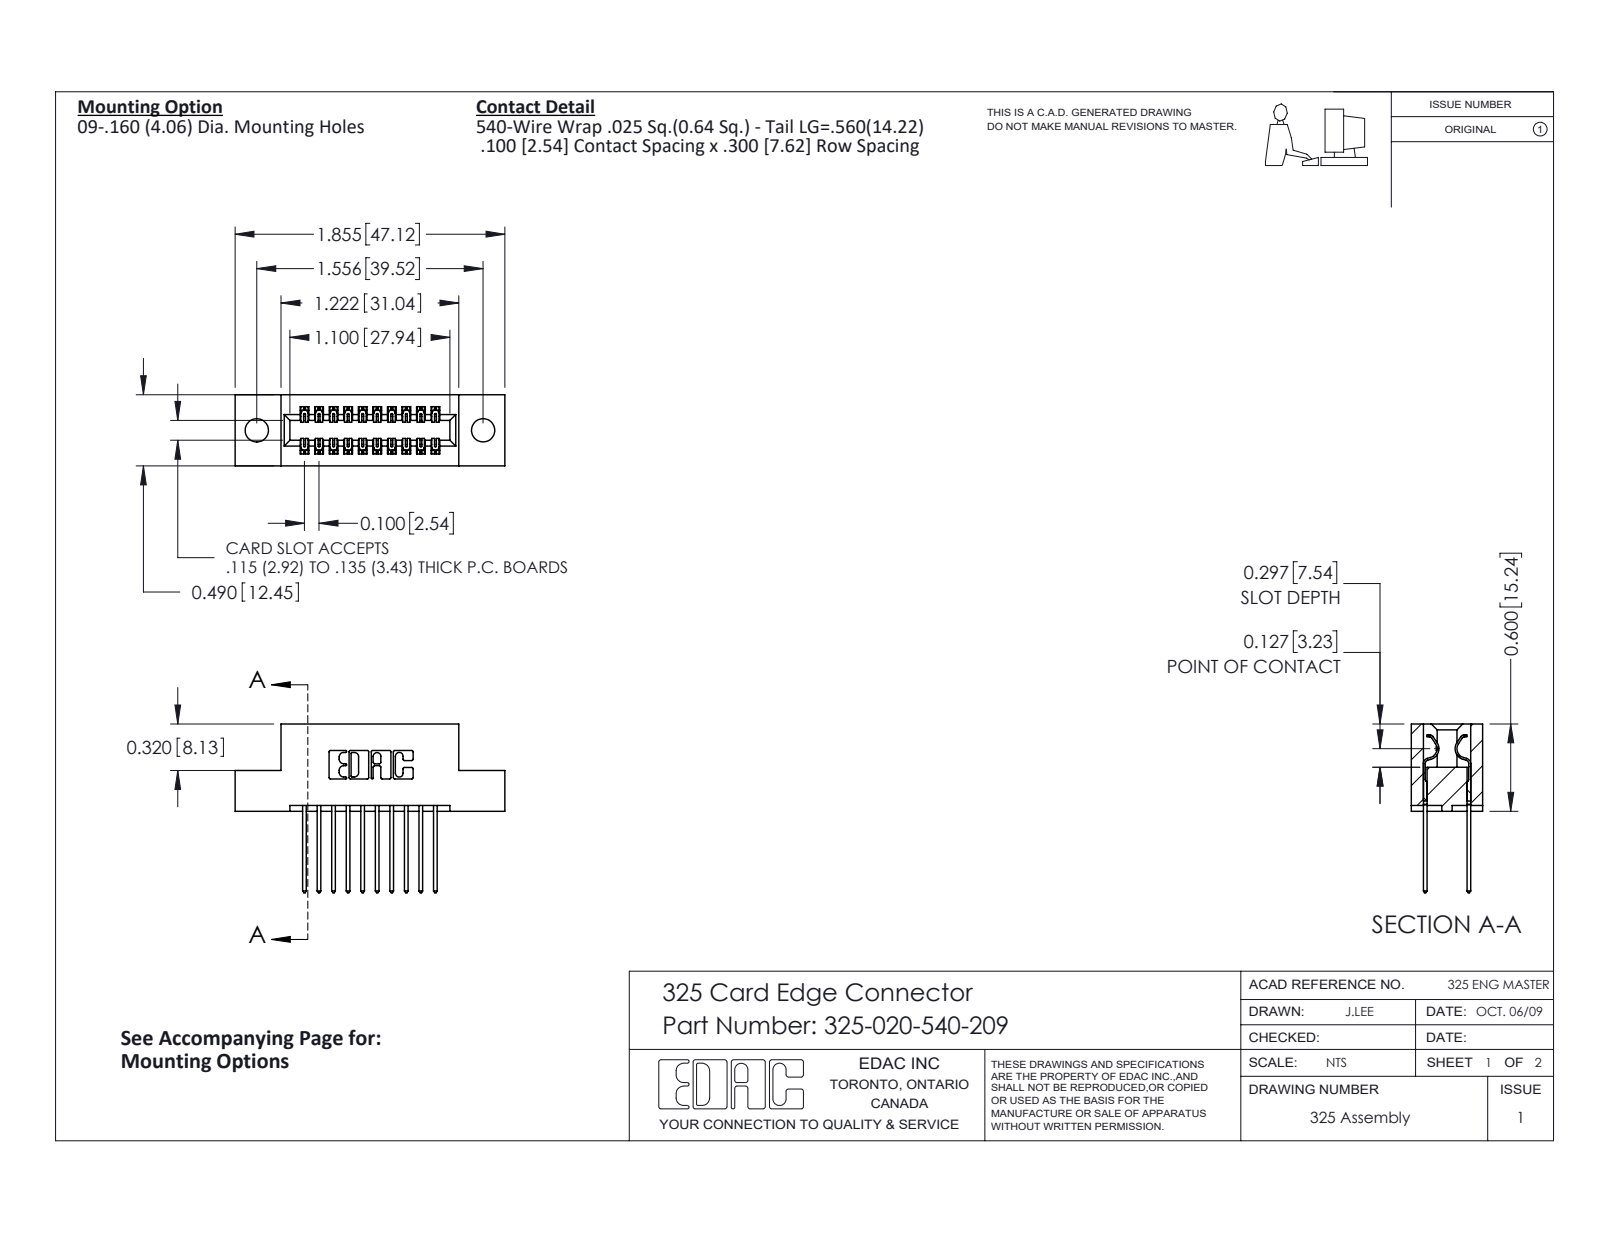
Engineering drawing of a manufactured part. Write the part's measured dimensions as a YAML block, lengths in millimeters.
part_name: "325 Part_.160 TH; 325-020-540-209; 325-292-001_325-293-140"
step_written_by: "SolidWorks 2016 (CONFIG_CONTROL_DESIGN)"
units: millimeters
bodies: {solids: 21, faces: 1154, planar: 790, cylindrical: 364, other: 0}
overall_size: [47.1, 29.5, 12.4]
volume: 5640
surface_area: 6350
round_holes:
  - {diameter: 4.1, count: 2}
partial_cylinders:
  - {radius: 0.2, count: 30}
  - {radius: 0.3, count: 22}
  - {radius: 0.3, count: 20}
  - {radius: 0.2, count: 6}
  - {radius: 0.8, count: 6}
  - {radius: 0.7, count: 3}
  - {radius: 0.4, count: 2}
  - {radius: 0.6, count: 2}
face_to_face_distances: [7.6, 2.1, 10.3, 1, 2.5, 12.4, 2.7, 9.7, 0.6, 5.1]
hole_center_spacings: [39.5]
